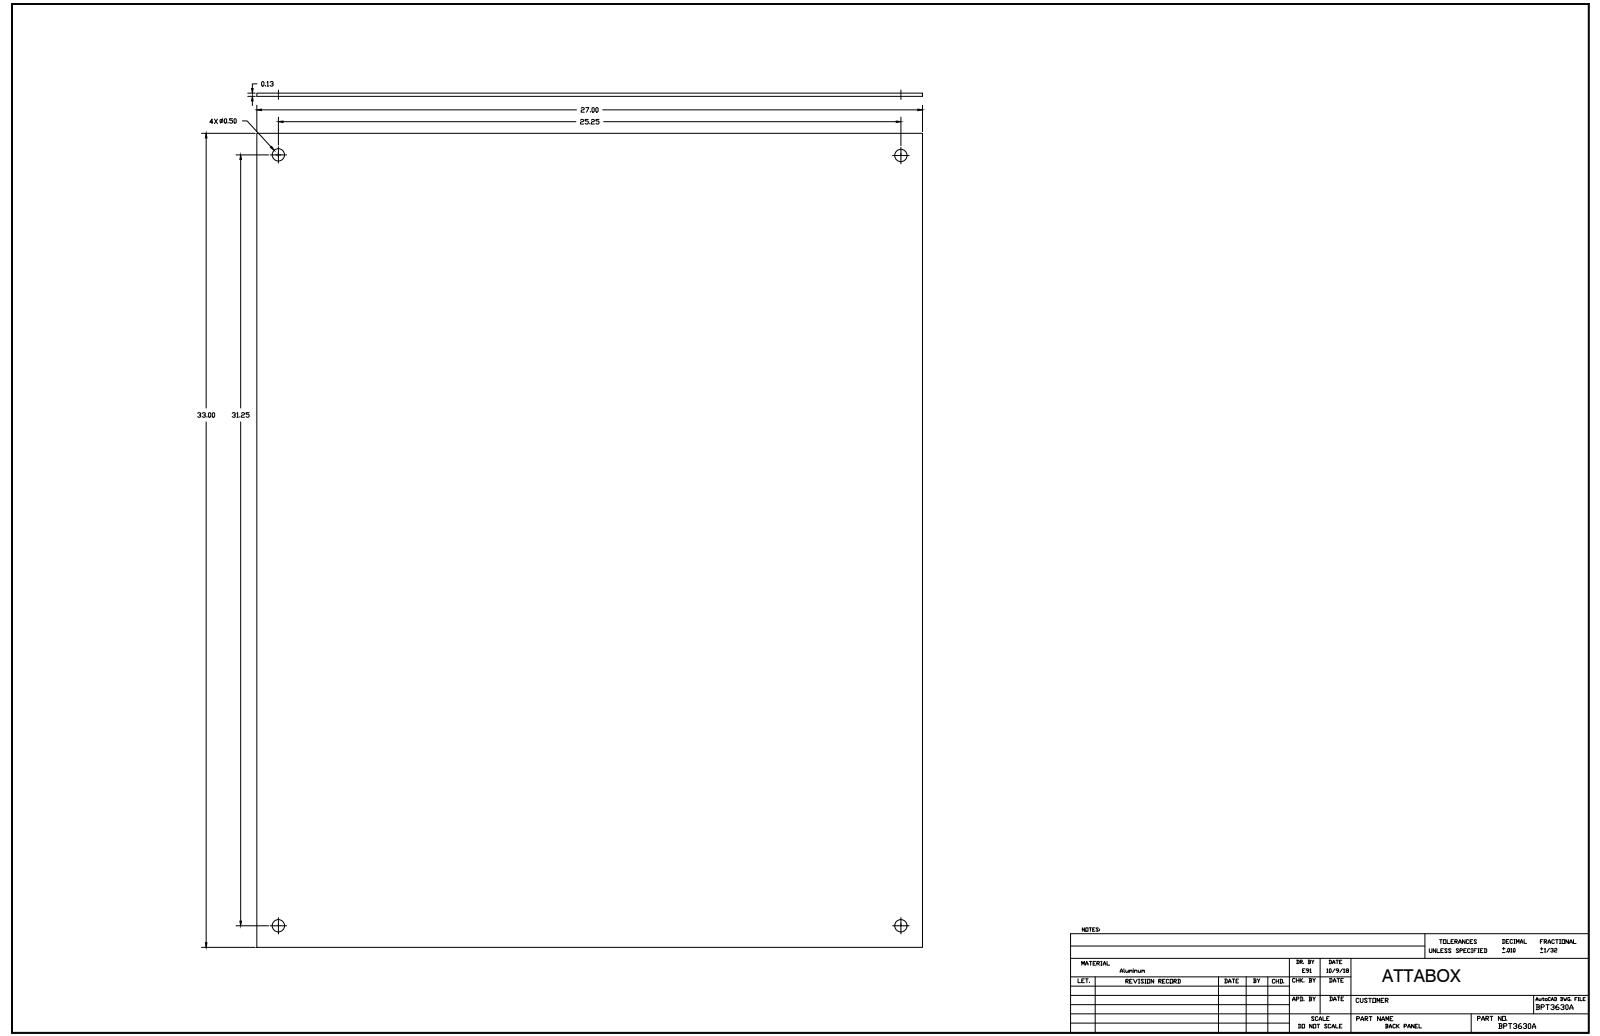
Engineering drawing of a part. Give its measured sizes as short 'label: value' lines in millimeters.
name: BP3630AL_STP
written by: Autodesk Inventor 2014 (AUTOMOTIVE_DESIGN)
unit: mm
bodies: 1 solid, 12 faces (6 planar, 6 cylindrical, 0 other)
size: 838.2 × 685.8 × 3.3
volume: 1 896 000 mm³; area: 1 159 000 mm²
holes: 6× ⌀12.7
face distances: 3.3, 685.8, 838.2
hole spacings: 396.88, 754.21, 641.34, 793.76, 1020.48
